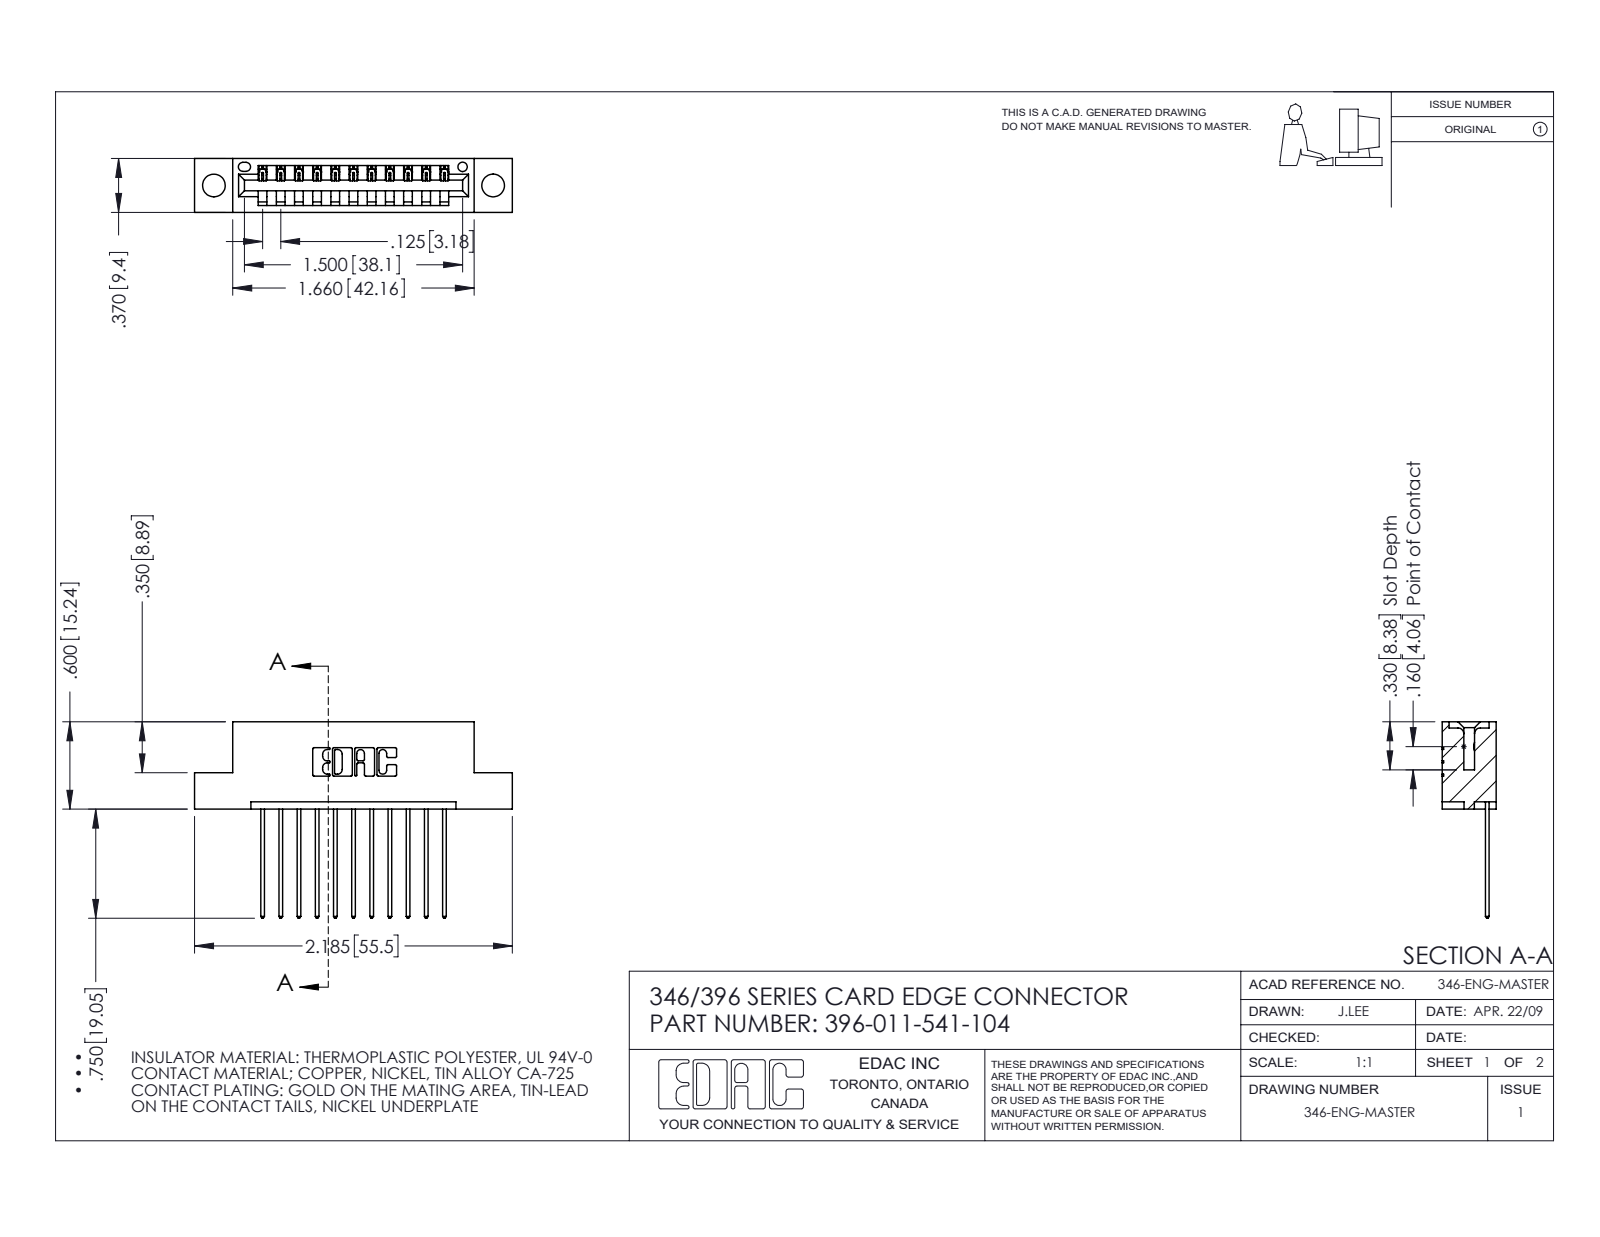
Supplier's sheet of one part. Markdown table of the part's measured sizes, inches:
| quantity | value |
| --- | --- |
| part name | 346 Part_Flush Mounting Lugs - 0.156 Dia-TH; 345-292-001_345-293-141; 396-011-541-104 |
| STEP written by | SolidWorks 2016 (CONFIG_CONTROL_DESIGN) |
| units | inches |
| bodies | 12 solids, 760 faces (516 planar, 244 cylindrical, 0 other) |
| overall size | 2.185 × 1.35 × 0.37 |
| volume | 0.308 in³ |
| surface area | 9.294 in² |
| round holes (diameter × count) | 0.156 × 2, 0.064 × 1 |
| partial cylindrical surfaces (radius × count) | 0.006 × 22, 0.01 × 22, 0.01 × 22, 0.007 × 6, 0.031 × 6, 0.026 × 3, 0.031 × 2, 0.04 × 2 |
| main face-to-face distances | 0.25, 0.048, 0.322, 0.37, 0.072, 0.298, 0.025, 0.148, 0.222, 0.1 |
| hole center spacings | 0.246, 1.715, 1.92 |
